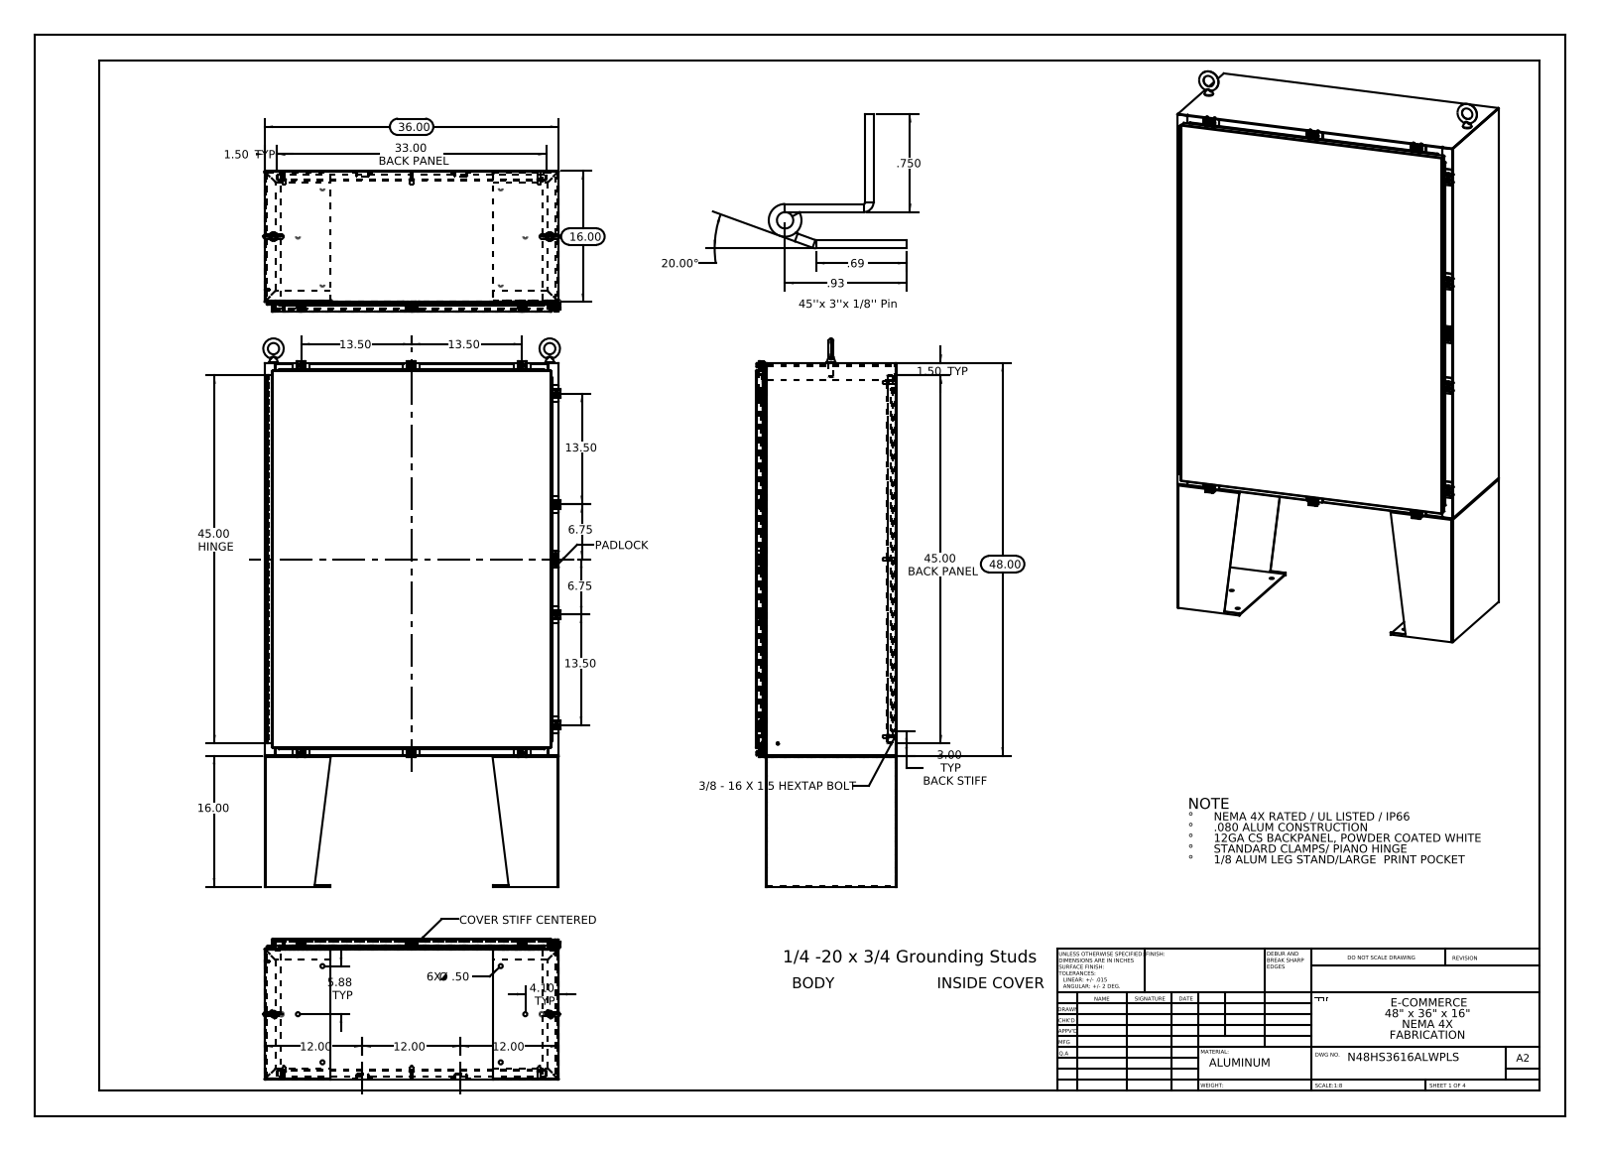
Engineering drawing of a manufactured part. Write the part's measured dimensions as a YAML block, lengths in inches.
part_name: "N48HS3616SSWPLS Padlock Staple; N48HS3616SSWPLS Clamp Bracket; Quarter-20 CD Stud; N48HS3616SSWPLS 125 Pin Hinge (+8 more)"
step_written_by: "SolidWorks 2013 (CONFIG_CONTROL_DESIGN)"
units: inches
bodies: {solids: 86, faces: 3235, planar: 1662, cylindrical: 1313, other: 260}
overall_size: [67, 36.346, 17.201]
volume: 851.5
surface_area: 20430
round_holes:
  - {diameter: 0.5, count: 14}
  - {diameter: 0.213, count: 10}
  - {diameter: 0.26, count: 10}
  - {diameter: 0.25, count: 6}
  - {diameter: 0.75, count: 4}
  - {diameter: 0.125, count: 2}
  - {diameter: 0.125, count: 1}
round_bosses_or_shafts:
  - {diameter: 0.25, count: 11}
  - {diameter: 0.625, count: 10}
  - {diameter: 0.5, count: 10}
  - {diameter: 0.399, count: 10}
  - {diameter: 0.375, count: 8}
  - {diameter: 0.33, count: 8}
  - {diameter: 0.157, count: 6}
  - {diameter: 0.14, count: 6}
partial_cylinders:
  - {radius: 0.06, count: 46}
  - {radius: 0.013, count: 39}
  - {radius: 0.088, count: 33}
  - {radius: 0.12, count: 20}
  - {radius: 0.141, count: 20}
  - {radius: 0.05, count: 15}
  - {radius: 0.08, count: 14}
  - {radius: 0.09, count: 14}
face_to_face_distances: [0.075, 17.126, 0.104, 17.051, 1.075, 35.925, 17.201, 1, 16.126, 16.051]
hole_center_spacings: [13.5, 8.393, 13.663, 20, 20.123, 21.625, 23.82, 25.48]
